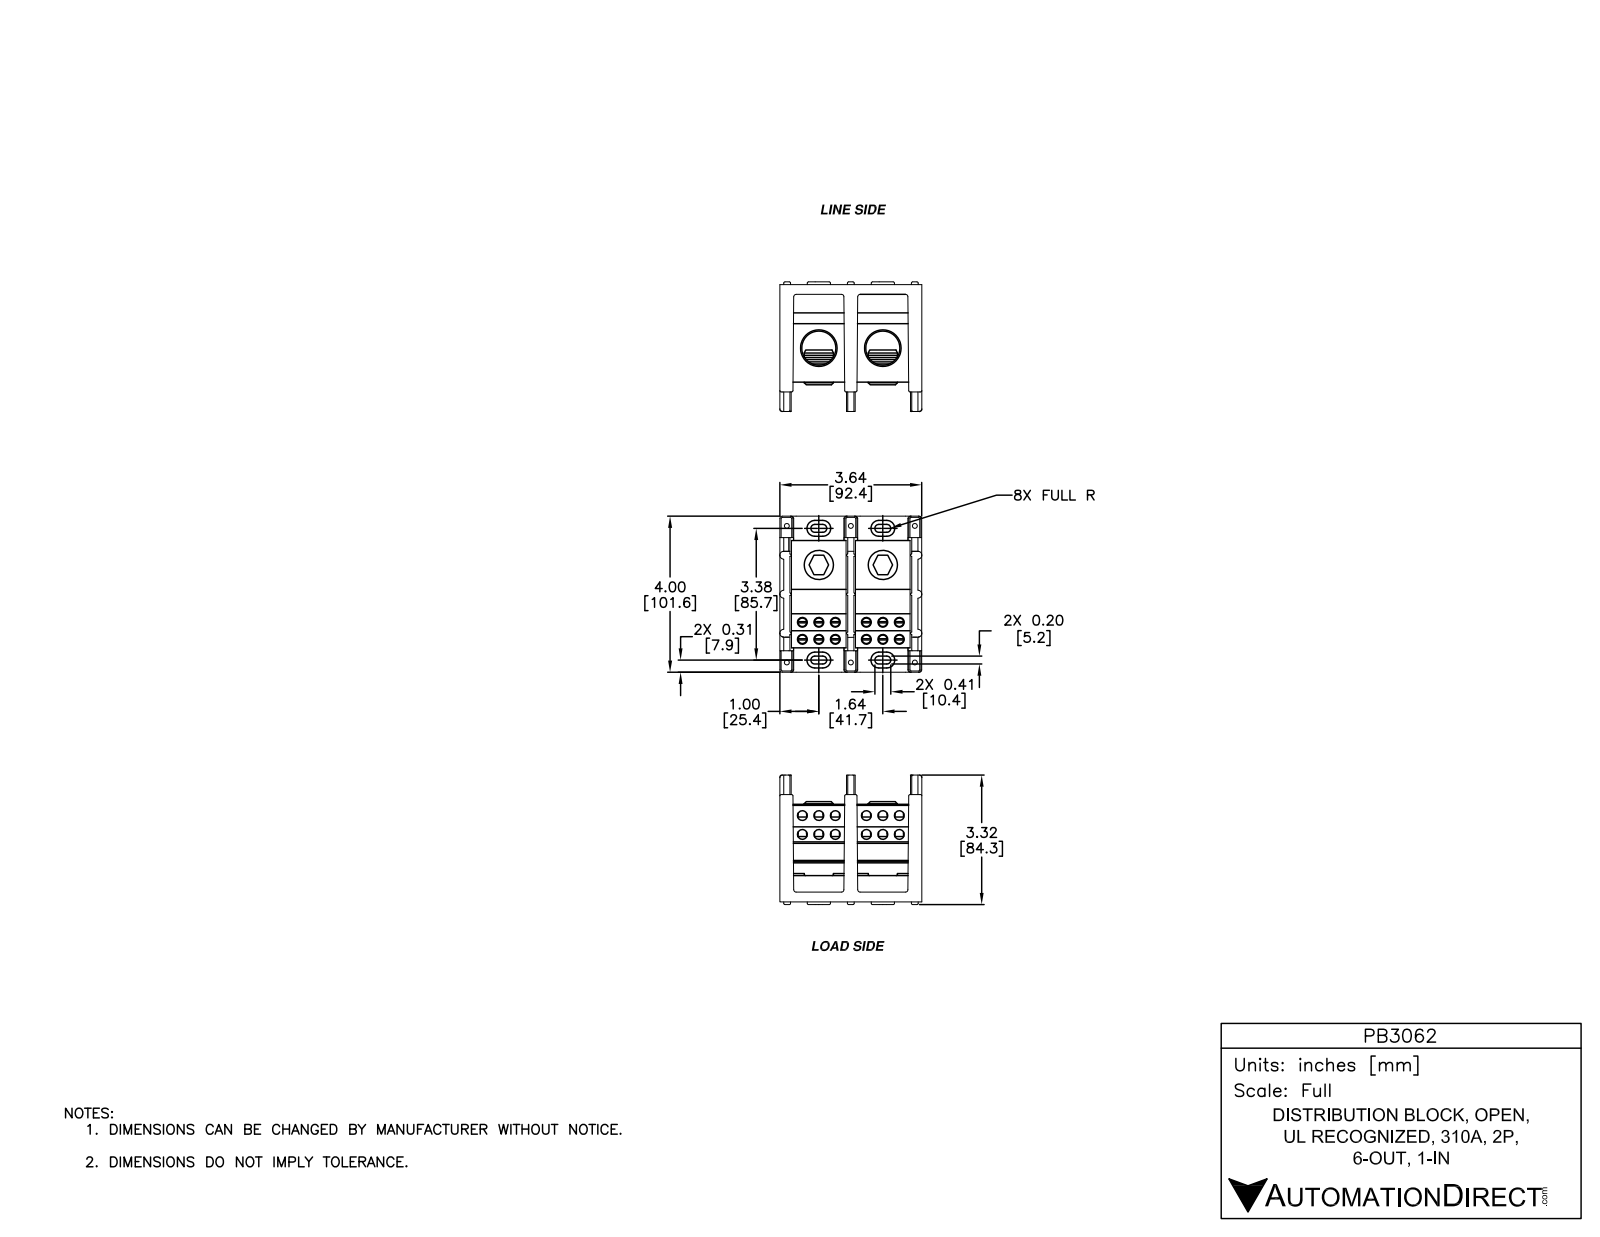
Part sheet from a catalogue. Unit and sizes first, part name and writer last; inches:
Units: inches
Overall size (bounding box): 4 × 3.641 × 3.35
Round holes (diameter × count): ⌀0.219 ×12, ⌀0.25 ×12, ⌀0.125 ×6, ⌀0.75 ×3, ⌀0.5 ×2, ⌀0.875 ×2
Round bosses / shafts (diameter × count): ⌀0.174 ×6, ⌀0.062 ×4, ⌀0.375 ×2
Partial cylindrical surfaces — rounded edges, fillets, slot ends (radius × count): R0.031 ×64, R0.1 ×38, R0.063 ×25, R0.062 ×20, R0.203 ×16, R0.094 ×8, R0.109 ×8
Main face-to-face distances: 1.641, 0.159, 1.481, 0.1, 1.8, 3.281, 1.9, 0.259, 1.741, 3.381
Hole centre spacings: 1.641, 0.422, 0.608, 0.641, 0.845, 1.219, 1.933, 2.063
Volume: 19.06 in³ · Surface area: 196.6 in²
Bodies: 7 solids, 1028 faces (417 planar, 427 cylindrical, 184 other)
Part name (STEP PRODUCT): PB3062
STEP written by: SolidWorks 2014 (AUTOMOTIVE_DESIGN)
